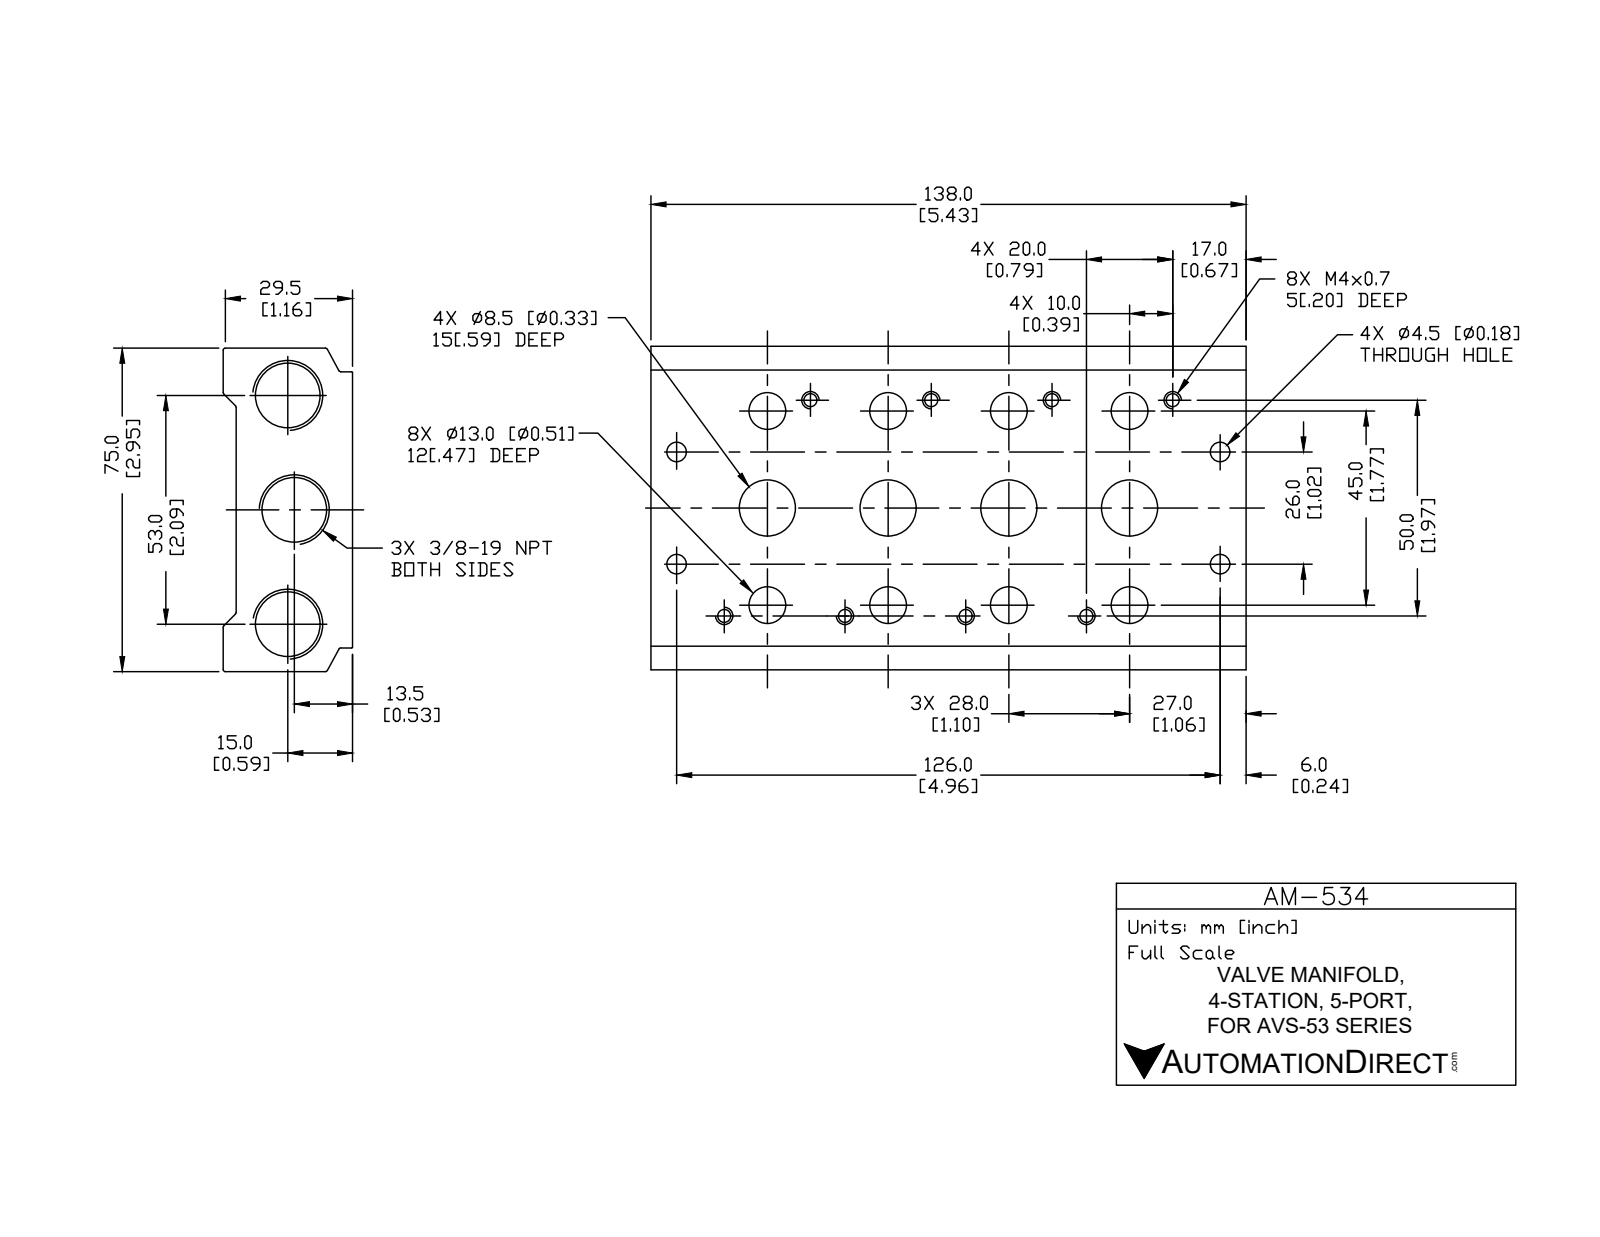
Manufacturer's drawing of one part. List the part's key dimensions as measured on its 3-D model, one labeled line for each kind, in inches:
Part name (STEP PRODUCT): AM-534
STEP written by: SolidWorks 2015 (CONFIG_CONTROL_DESIGN)
Units: inches
Bodies: 1 solid, 129 faces (36 planar, 65 cylindrical, 28 other)
Overall size (bounding box): 5.433 × 2.953 × 1.181
Volume: 12.51 in³ · Surface area: 84.2 in²
Round holes (diameter × count): ⌀0.13 ×8, ⌀0.335 ×8, ⌀0.177 ×4, ⌀0.512 ×4, ⌀0.562 ×3
Partial cylindrical surfaces — rounded edges, fillets, slot ends (radius × count): R0.02 ×11
Main face-to-face distances: 1.063, 2.953, 0.118, 1.181, 5.433, 0.407, 5.026, 0.236, 2.717, 4.62
Hole centre spacings: 1.102, 1.414, 2.205, 0.406, 0.886, 1.06, 1.911, 2.376
